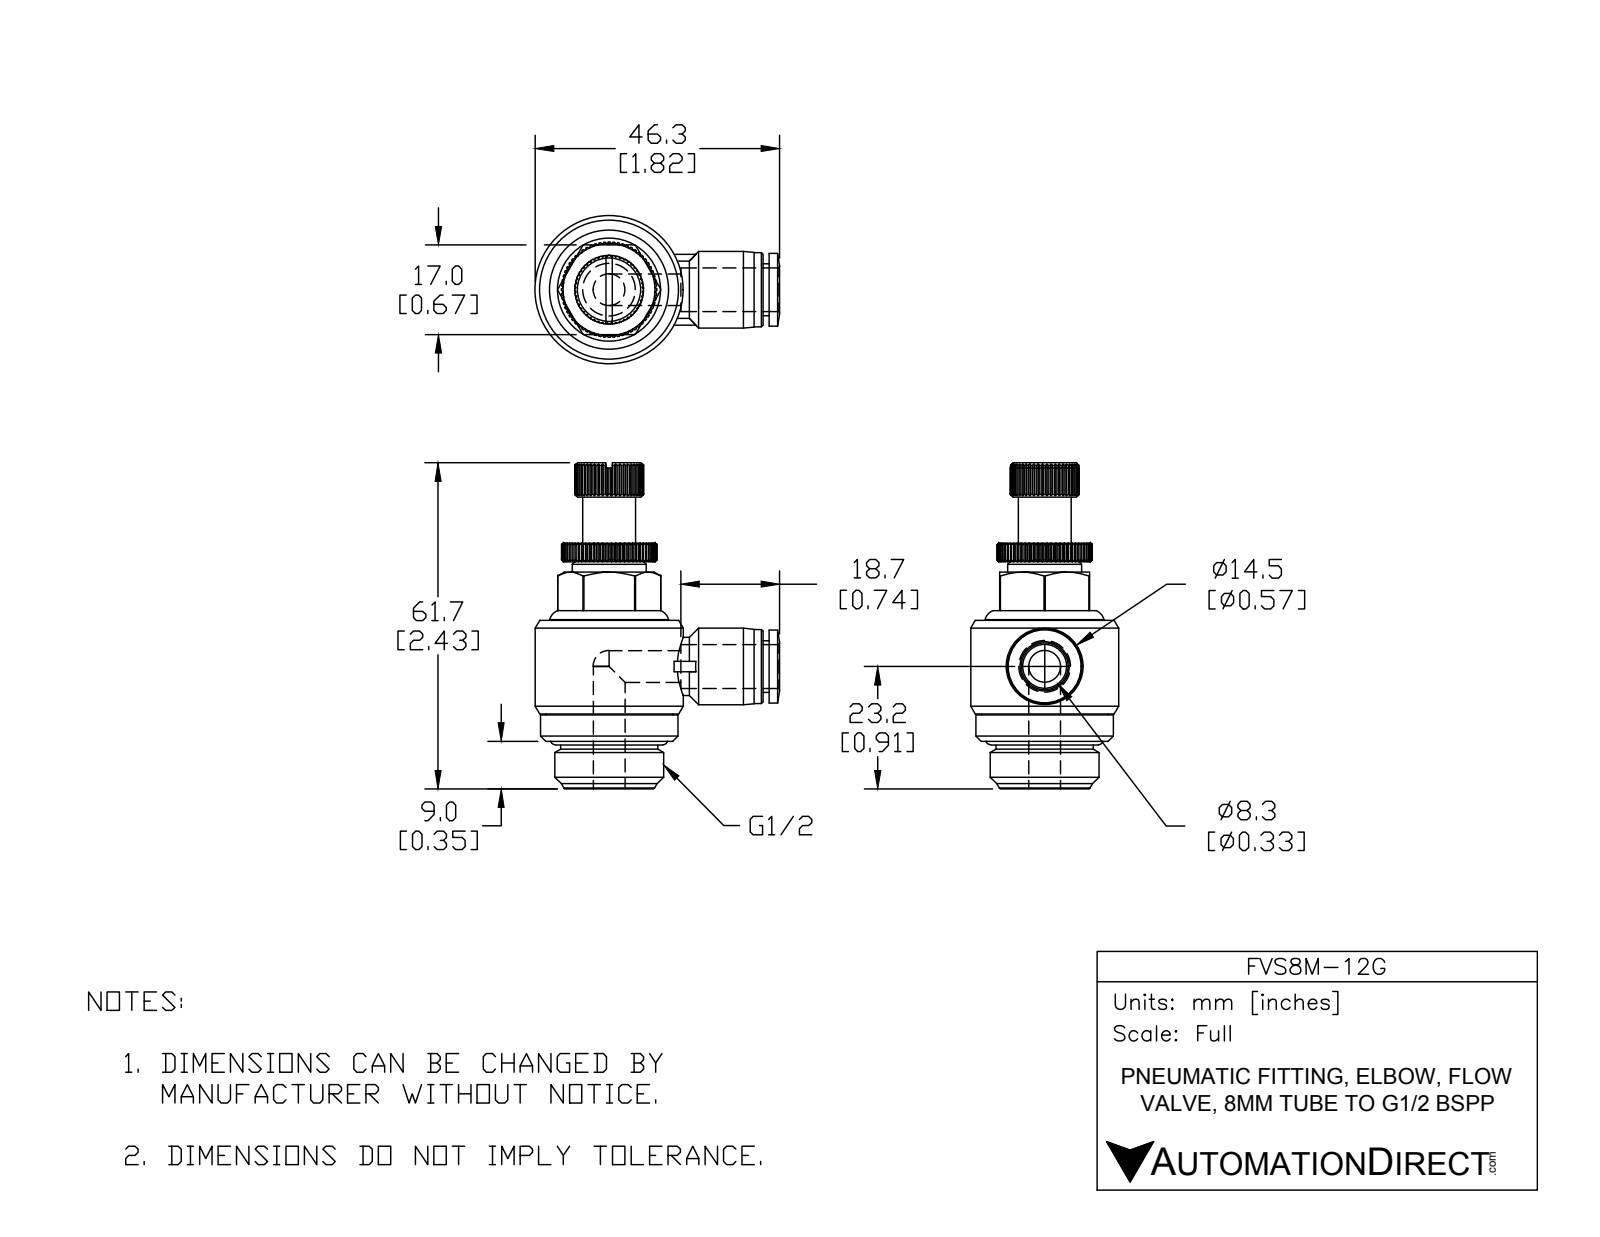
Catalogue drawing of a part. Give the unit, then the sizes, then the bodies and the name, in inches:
Units: inches
Overall size (bounding box): 2.429 × 1.821 × 1.102
Round holes (diameter × count): ⌀0.236 ×2, ⌀0.327 ×1
Round bosses / shafts (diameter × count): ⌀0.551 ×2, ⌀1.102 ×1, ⌀1.024 ×1, ⌀0.945 ×1, ⌀0.864 ×1, ⌀0.811 ×1, ⌀0.724 ×1, ⌀0.571 ×1
Partial cylindrical surfaces — rounded edges, fillets, slot ends (radius × count): R0.256 ×1, R0.354 ×1, R0.384 ×1
Main face-to-face distances: 0.669, 1.256, 1.831, 0.575, 0.598, 1.693, 0.437, 0.138, 0.736, 0.557
Volume: 1.35 in³ · Surface area: 12.64 in²
Bodies: 2 solids, 599 faces (263 planar, 153 cylindrical, 183 other)
Part name (STEP PRODUCT): FVS8M-12G
STEP written by: SolidWorks 2015 (AUTOMOTIVE_DESIGN)
